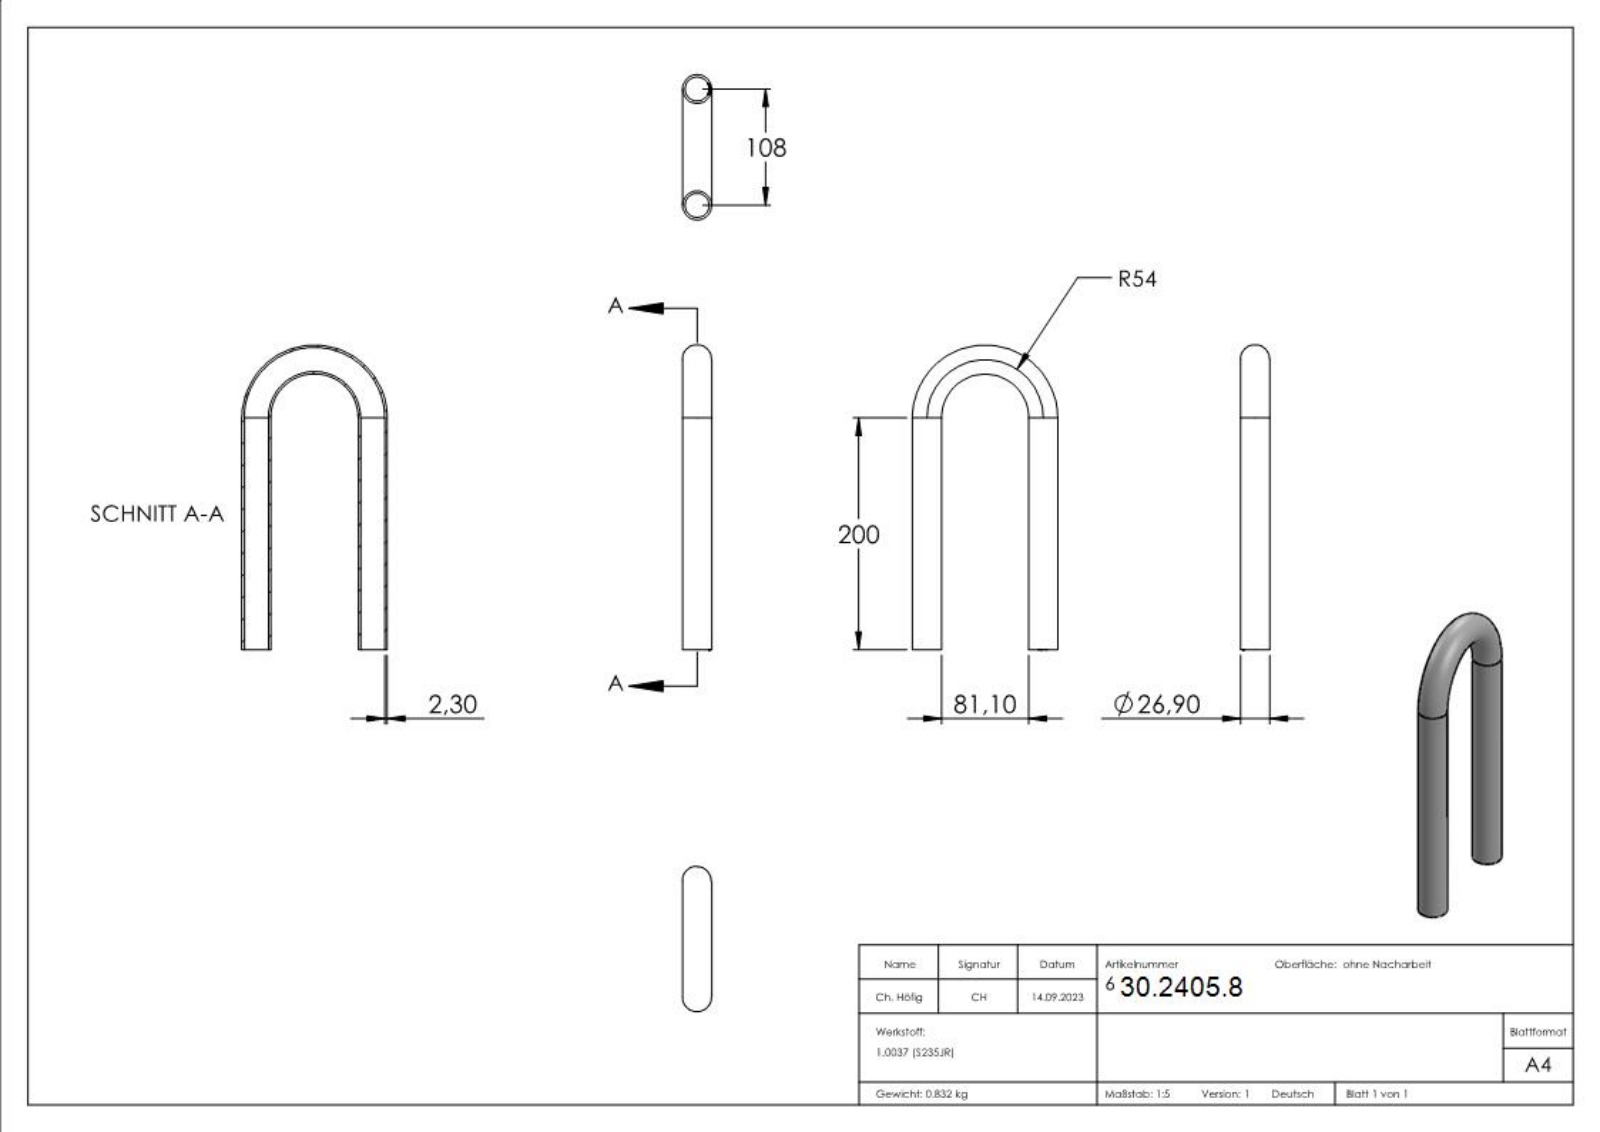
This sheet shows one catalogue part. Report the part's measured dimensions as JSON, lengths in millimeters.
{"part_name": "6965-180", "step_written_by": "SolidWorks 2018 (CONFIG_CONTROL_DESIGN)", "units": "millimeters", "bodies": {"solids": 1, "faces": 221, "planar": 106, "cylindrical": 4, "other": 111}, "overall_size": [282.63, 134.9, 26.9], "volume_mm3": 106651, "surface_area_mm2": 93101, "round_holes": [[22.3, 2]], "round_bosses_or_shafts": [[26.9, 2]], "face_to_face_distances": [0.51, 0.32, 0.8, 0.36, 0.88, 0.44, 0.43, 0.47, 0.33, 0.41], "hole_center_spacings": [108]}
